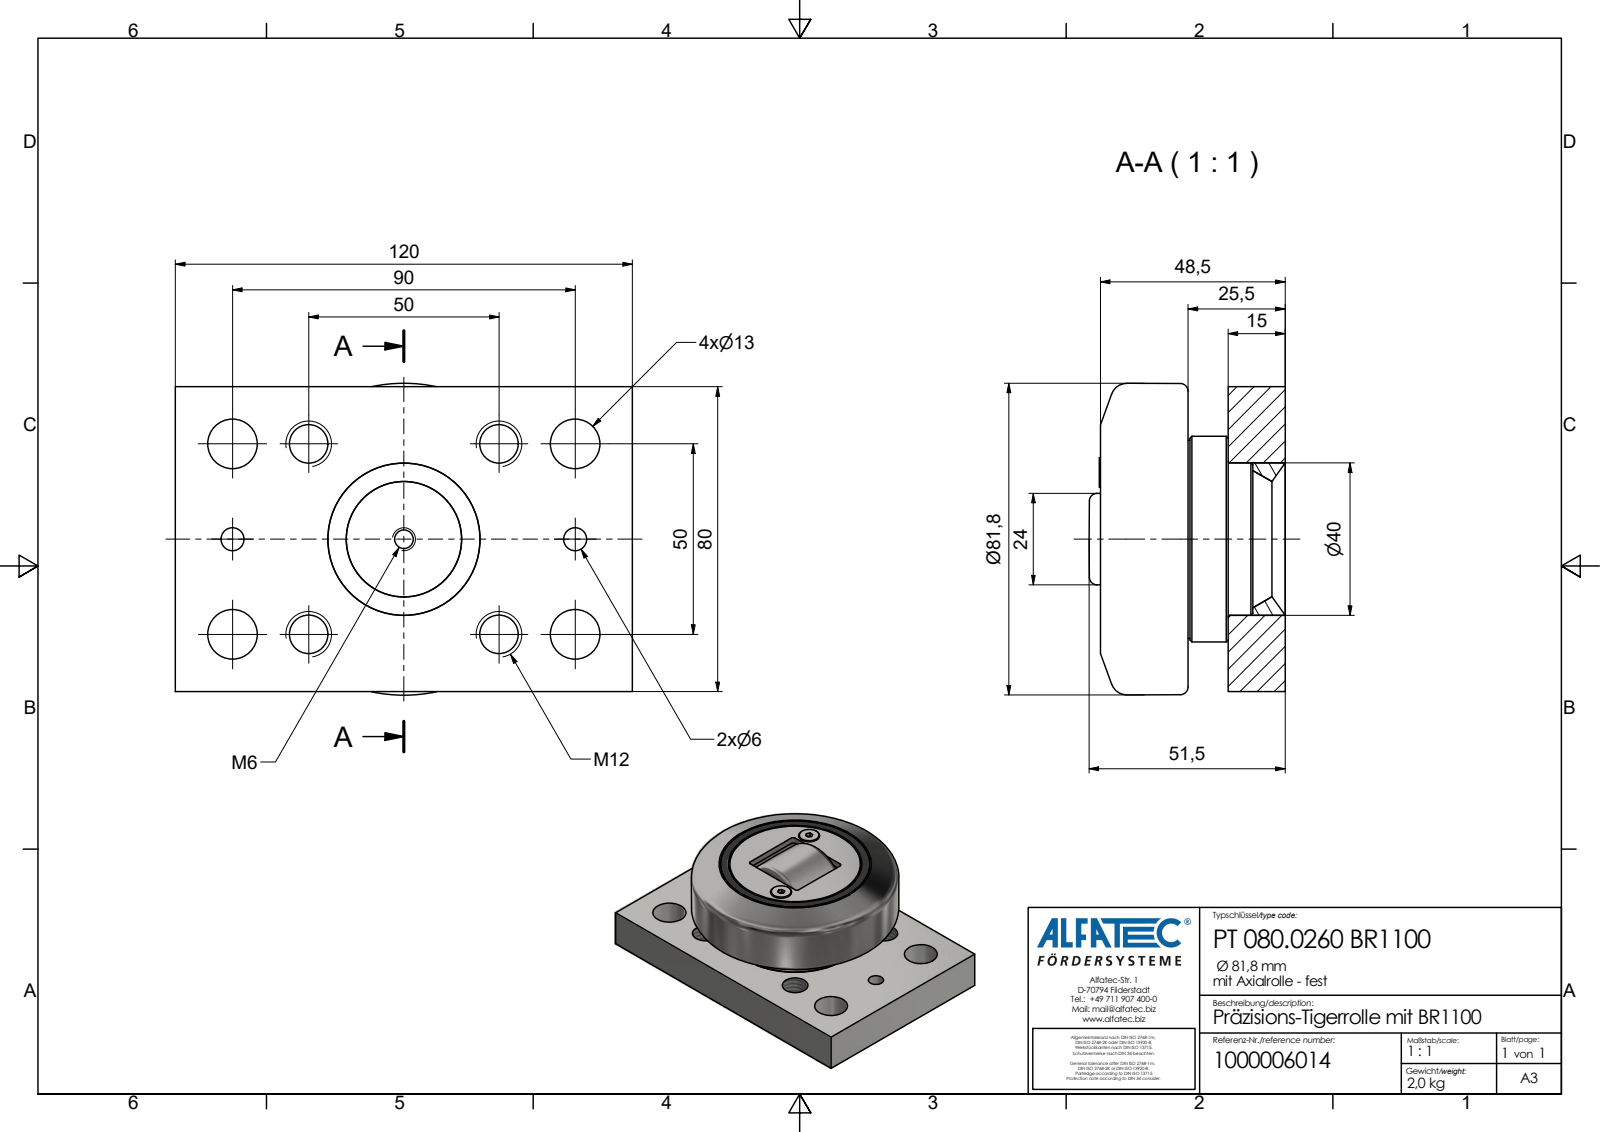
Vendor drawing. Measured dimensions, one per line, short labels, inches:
name: PT 080.0260 BR1100_Kontur
written by: Autodesk Inventor 2020 (AP242_MANAGED_MODEL_BASED_3D_ENGINEERING_MIM_LF)
unit: in
bodies: 1 solid, 60 faces (32 planar, 18 cylindrical, 10 other)
size: 4.724 × 3.22 × 2.028
volume: 16.27 in³; area: 64.46 in²
holes: 4× ⌀0.398, 4× ⌀0.512, 2× ⌀0.236, 1× ⌀0.098, 1× ⌀0.194
bosses: 2× ⌀0.307, 1× ⌀2.126, 1× ⌀2.047
rounds: 1× R0.059, 1× R0.906
face distances: 0.591, 1.004, 0.413, 1.909, 1.319, 0.906, 3.15, 4.724, 0.453, 0.138
hole spacings: 1.969, 0.787, 0.984, 1.261, 1.392, 2.027, 2.12, 2.756
